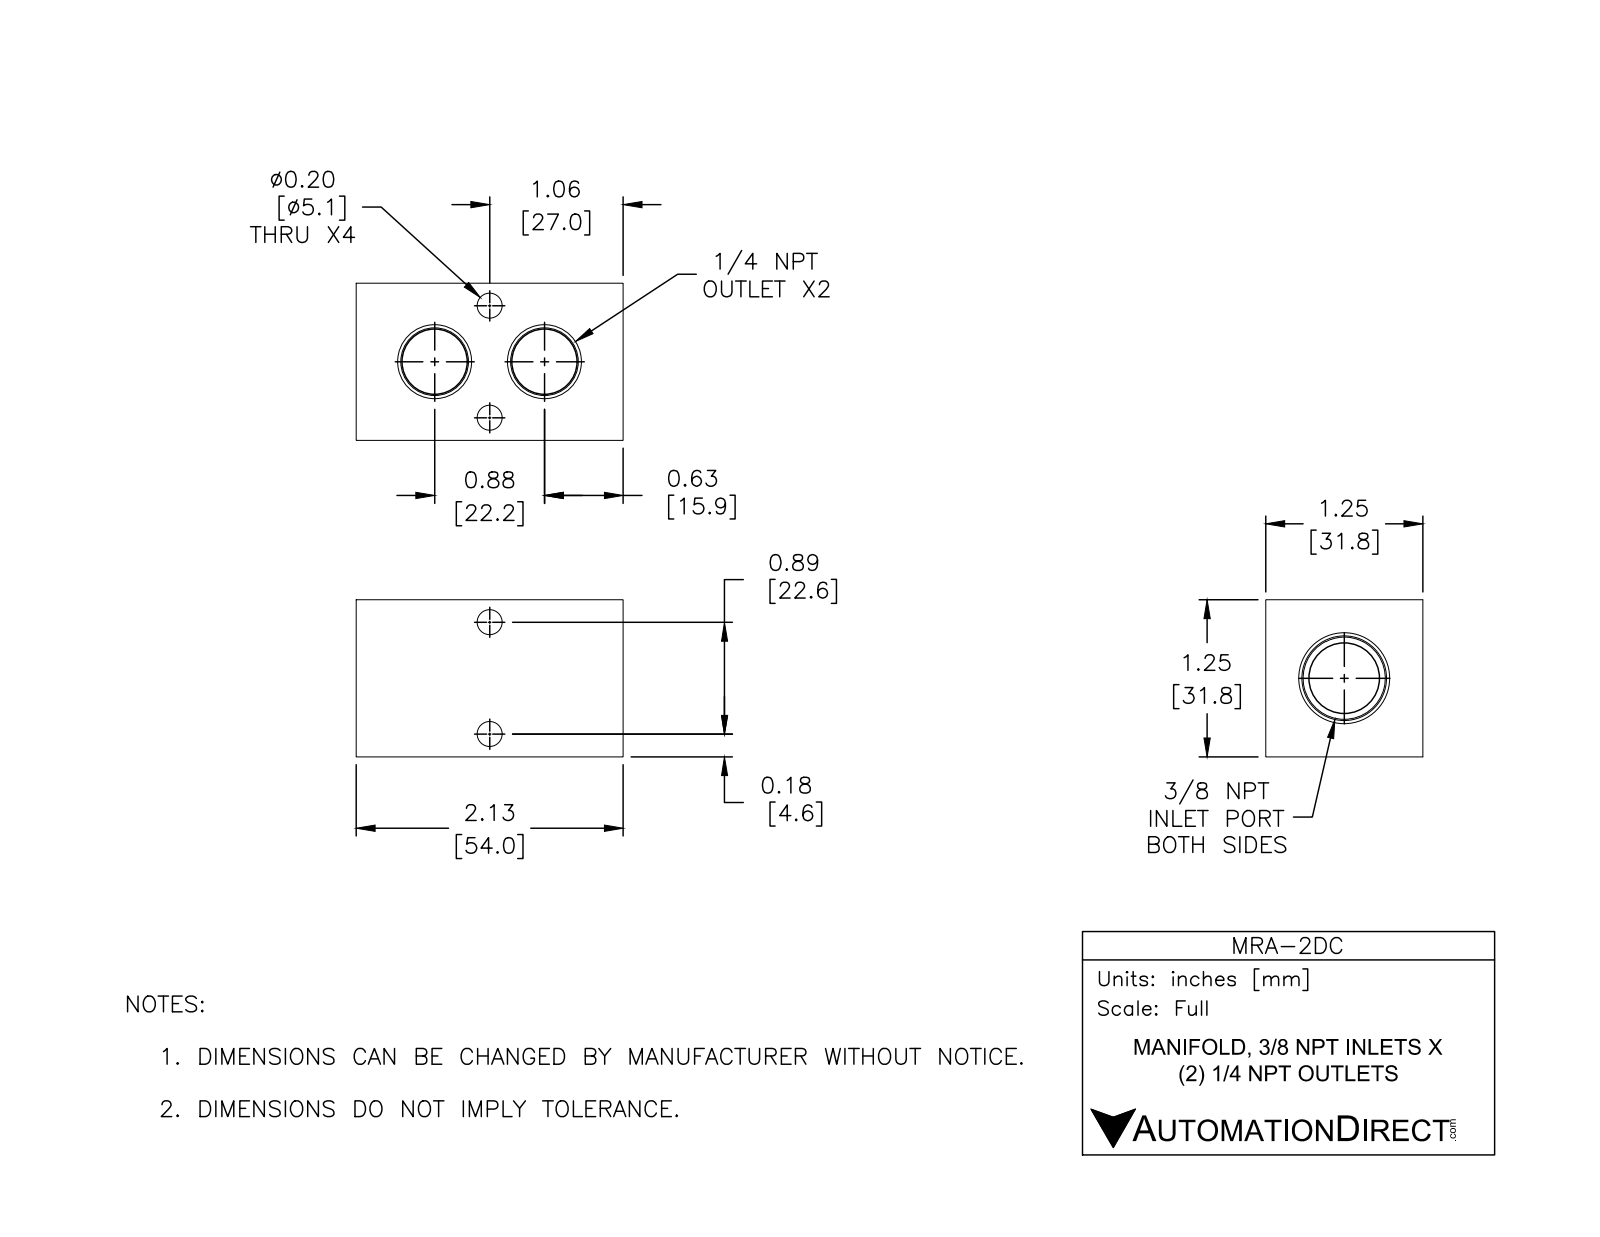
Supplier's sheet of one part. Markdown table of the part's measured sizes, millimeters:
| quantity | value |
| --- | --- |
| part name | MRA-2DC |
| STEP written by | SolidWorks 2015 (CONFIG_CONTROL_DESIGN) |
| units | millimeters |
| bodies | 1 solid, 58 faces (12 planar, 30 cylindrical, 16 other) |
| overall size | 54 × 31.8 × 31.8 |
| volume | 39 530 mm³ |
| surface area | 12 790 mm² |
| round holes (diameter × count) | 5.1 × 4, 14.3 × 1 |
| partial cylindrical surfaces (radius × count) | 5.6 × 2 |
| main face-to-face distances | 31.8, 54, 10.4, 43.6, 33.1, 21.8, 9.9 |
| hole center spacings | 22.6 |
